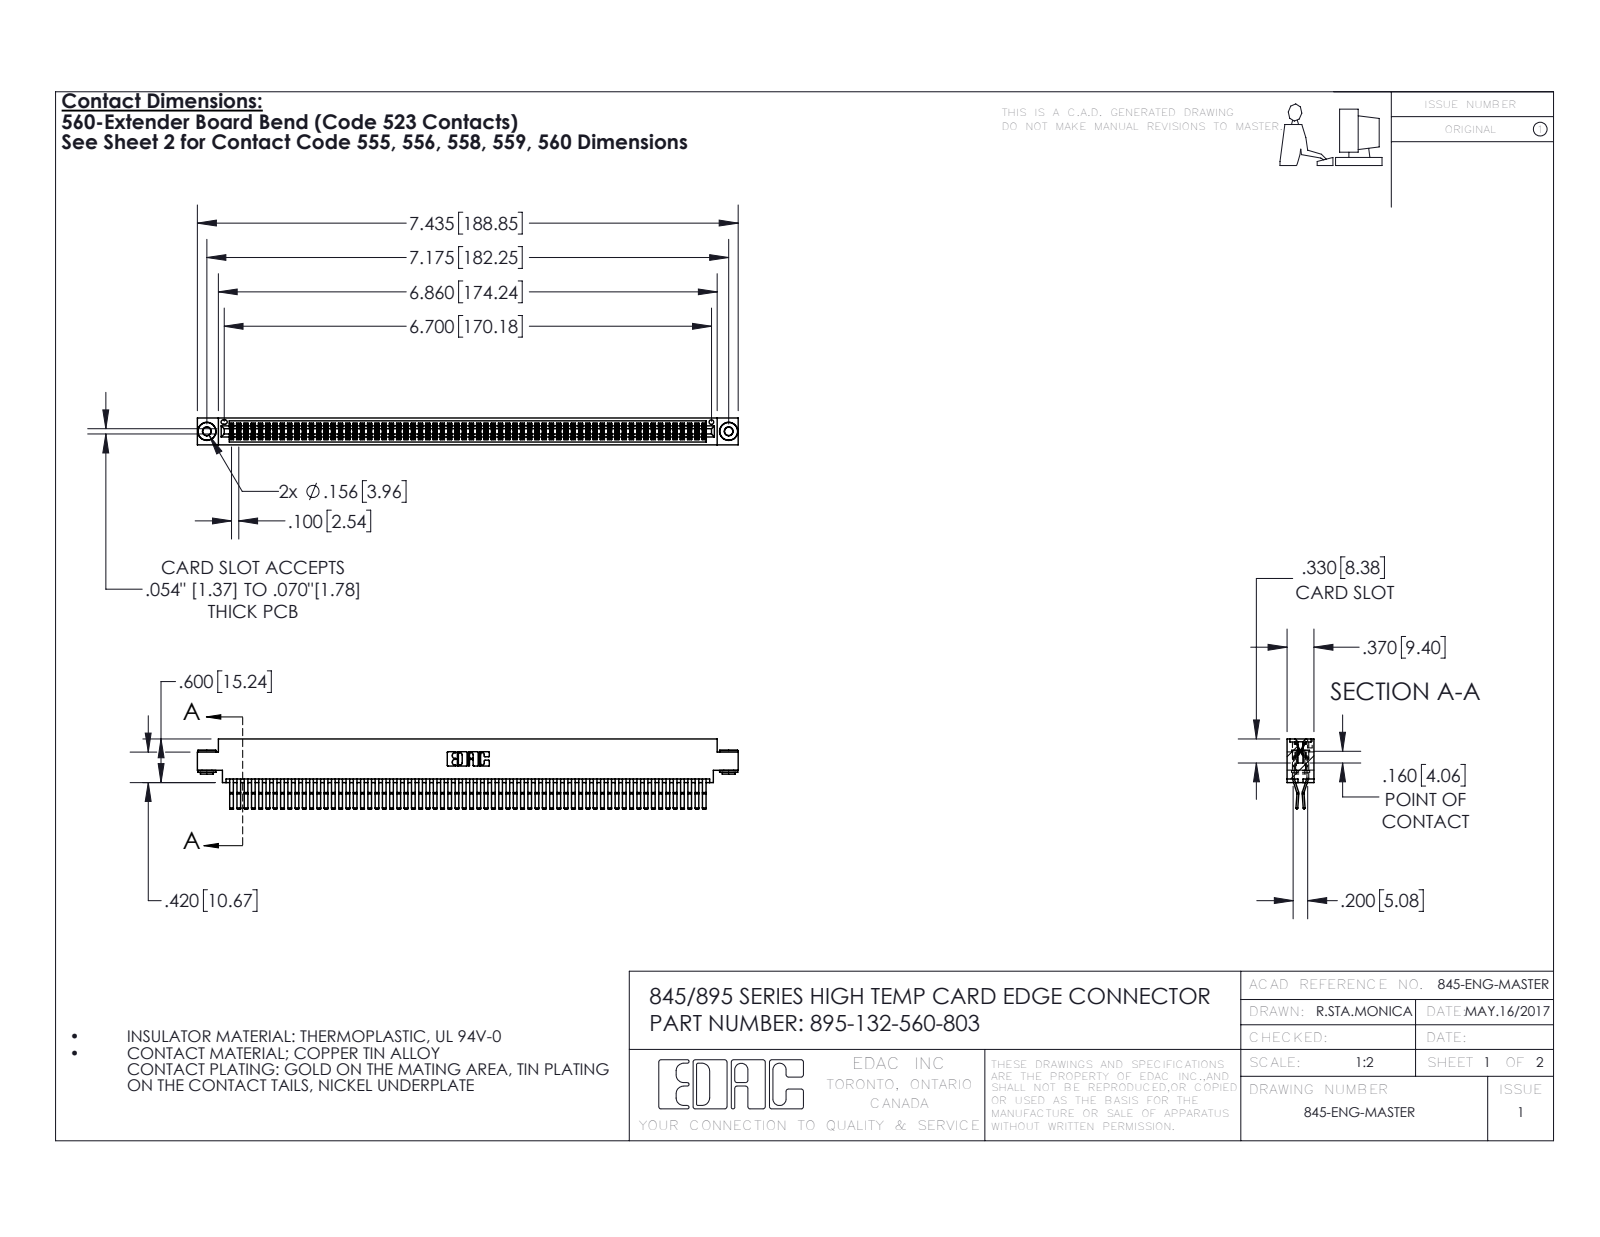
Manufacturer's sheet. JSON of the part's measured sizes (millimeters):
{"part_name": "395-132-560-803; 345 Part_0.170 Offset - 0.156 Dia-TH; 345-292-001_560 Tail; 345-250-002_345-250-002-102", "step_written_by": "SolidWorks 2016 (CONFIG_CONTROL_DESIGN)", "units": "millimeters", "bodies": {"solids": 135, "faces": 7032, "planar": 4450, "cylindrical": 2574, "other": 8}, "overall_size": [188.8, 24.4, 9.4], "volume_mm3": 19340, "surface_area_mm2": 31630, "round_holes": [[2.9, 2], [4, 2], [1.6, 1]], "round_bosses_or_shafts": [[6.4, 2], [4.6, 2], [3.5, 2]], "partial_cylinders_radius": [[0.2, 198], [0.3, 22], [0.2, 6], [0.8, 6], [0.7, 3], [0.3, 2], [0.4, 2], [0.5, 2]], "face_to_face_distances": [0.6, 1.8, 7.6, 9.4, 5.1, 2.5, 6.9, 5.7, 4.4, 3.8], "hole_center_spacings": [6.9, 176.3, 182.2]}
